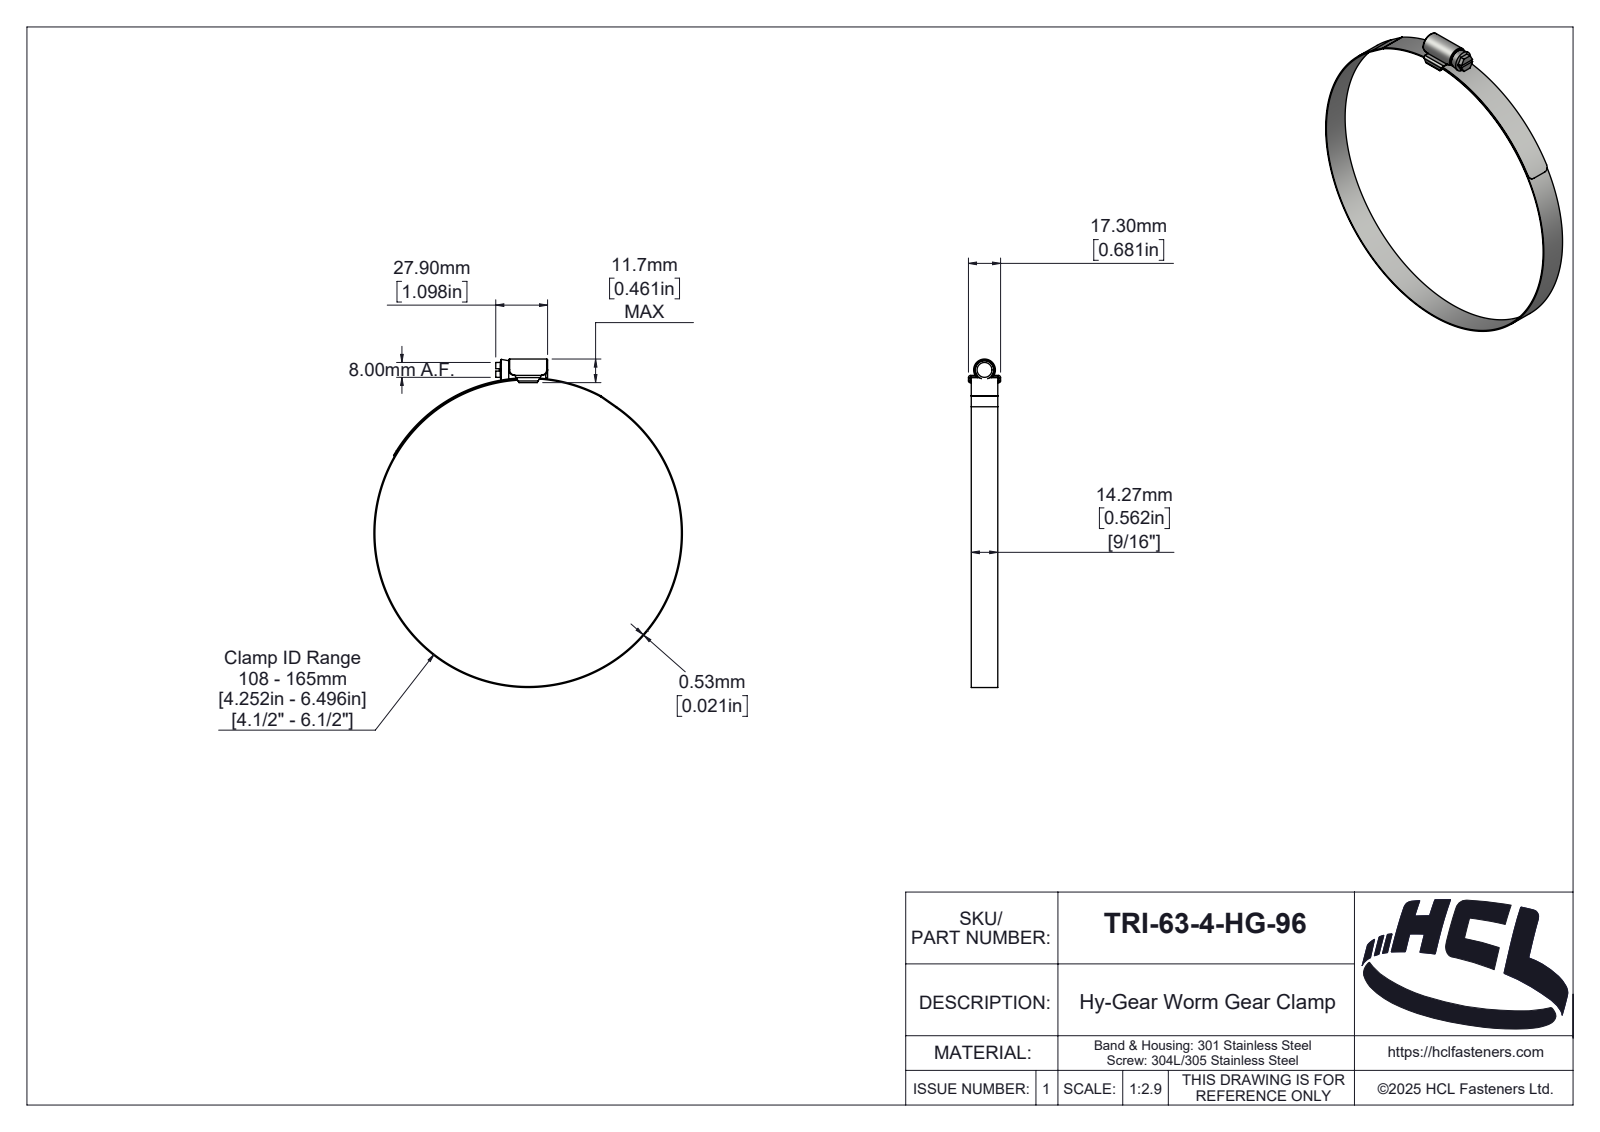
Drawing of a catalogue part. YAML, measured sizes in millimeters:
part_name: "TRI-50-0-HG-96"
step_written_by: "SolidWorks 2025 (AUTOMOTIVE_DESIGN)"
units: millimeters
bodies: {solids: 3, faces: 189, planar: 39, cylindrical: 89, other: 61}
overall_size: [176.73, 166.06, 17.3]
volume: 7386
surface_area: 20787
round_holes:
  - {diameter: 165, count: 1}
round_bosses_or_shafts:
  - {diameter: 166.06, count: 1}
  - {diameter: 10, count: 1}
partial_cylinders:
  - {radius: 0.5, count: 6}
  - {radius: 3, count: 4}
  - {radius: 0.1, count: 2}
  - {radius: 0.9, count: 2}
  - {radius: 1.2, count: 2}
  - {radius: 0.46, count: 1}
  - {radius: 1.89, count: 1}
  - {radius: 2, count: 1}
face_to_face_distances: [14.26, 0.8, 3.1, 0.53, 2.3, 3.9, 27.9, 1.52, 15.78, 16.5]
